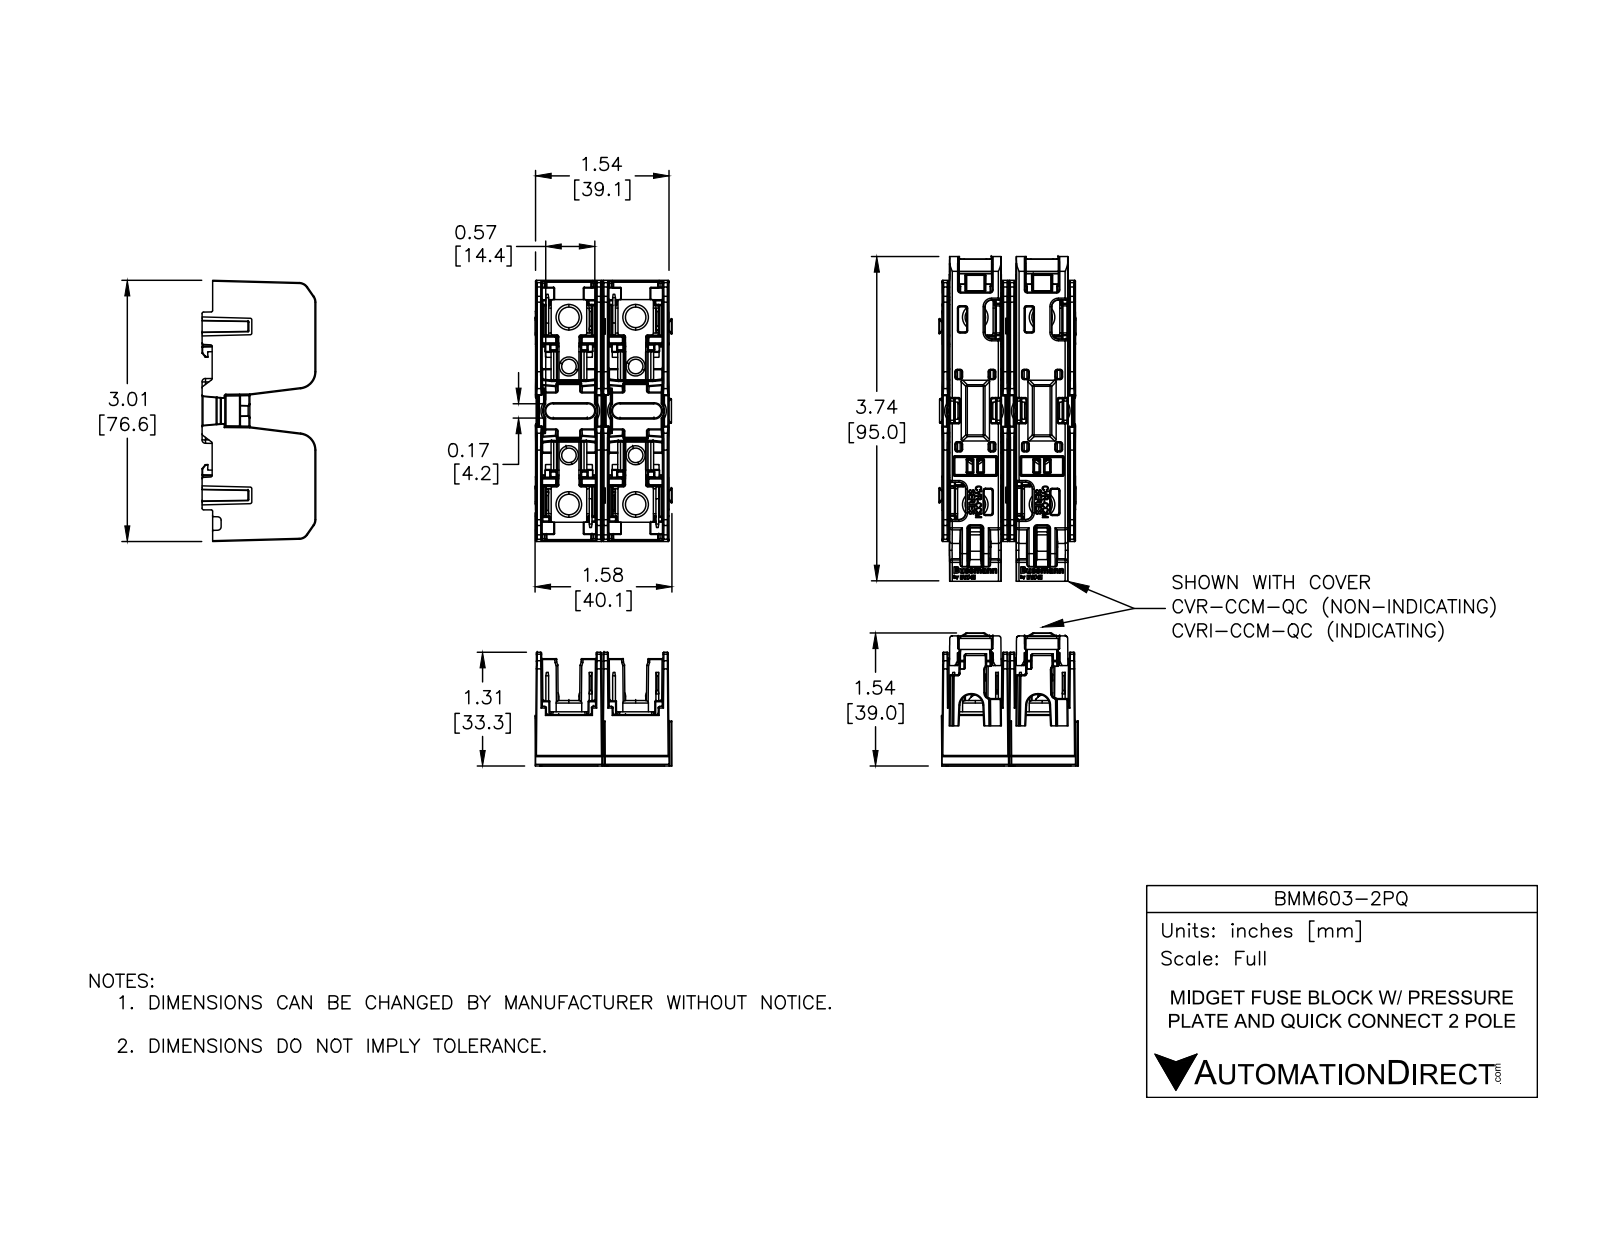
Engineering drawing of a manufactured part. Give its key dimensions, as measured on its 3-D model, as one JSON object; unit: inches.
{"part_name": "BMM603-2PQ", "step_written_by": "SolidWorks 2021 (CONFIG_CONTROL_DESIGN)", "units": "inches", "bodies": {"solids": 9, "faces": 977, "planar": 685, "cylindrical": 186, "other": 106}, "overall_size": [3.015, 1.578, 1.312], "volume_in3": 2.481, "surface_area_in2": 51.89, "round_holes": [[0.075, 4], [0.142, 4]], "round_bosses_or_shafts": [[0.295, 4], [0.22, 3], [0.138, 3]], "partial_cylinders_radius": [[0.004, 24], [0.02, 24], [0.01, 4], [0.03, 4], [0.053, 4], [0.061, 4], [0.084, 4], [0.085, 4]], "face_to_face_distances": [0.768, 0.691, 0.691, 0.594, 0.032, 0.588, 0.077, 1.458, 1.459, 0.077], "hole_center_spacings": [0.119, 0.768, 1.025, 1.281, 2.232, 2.124, 2.339]}
